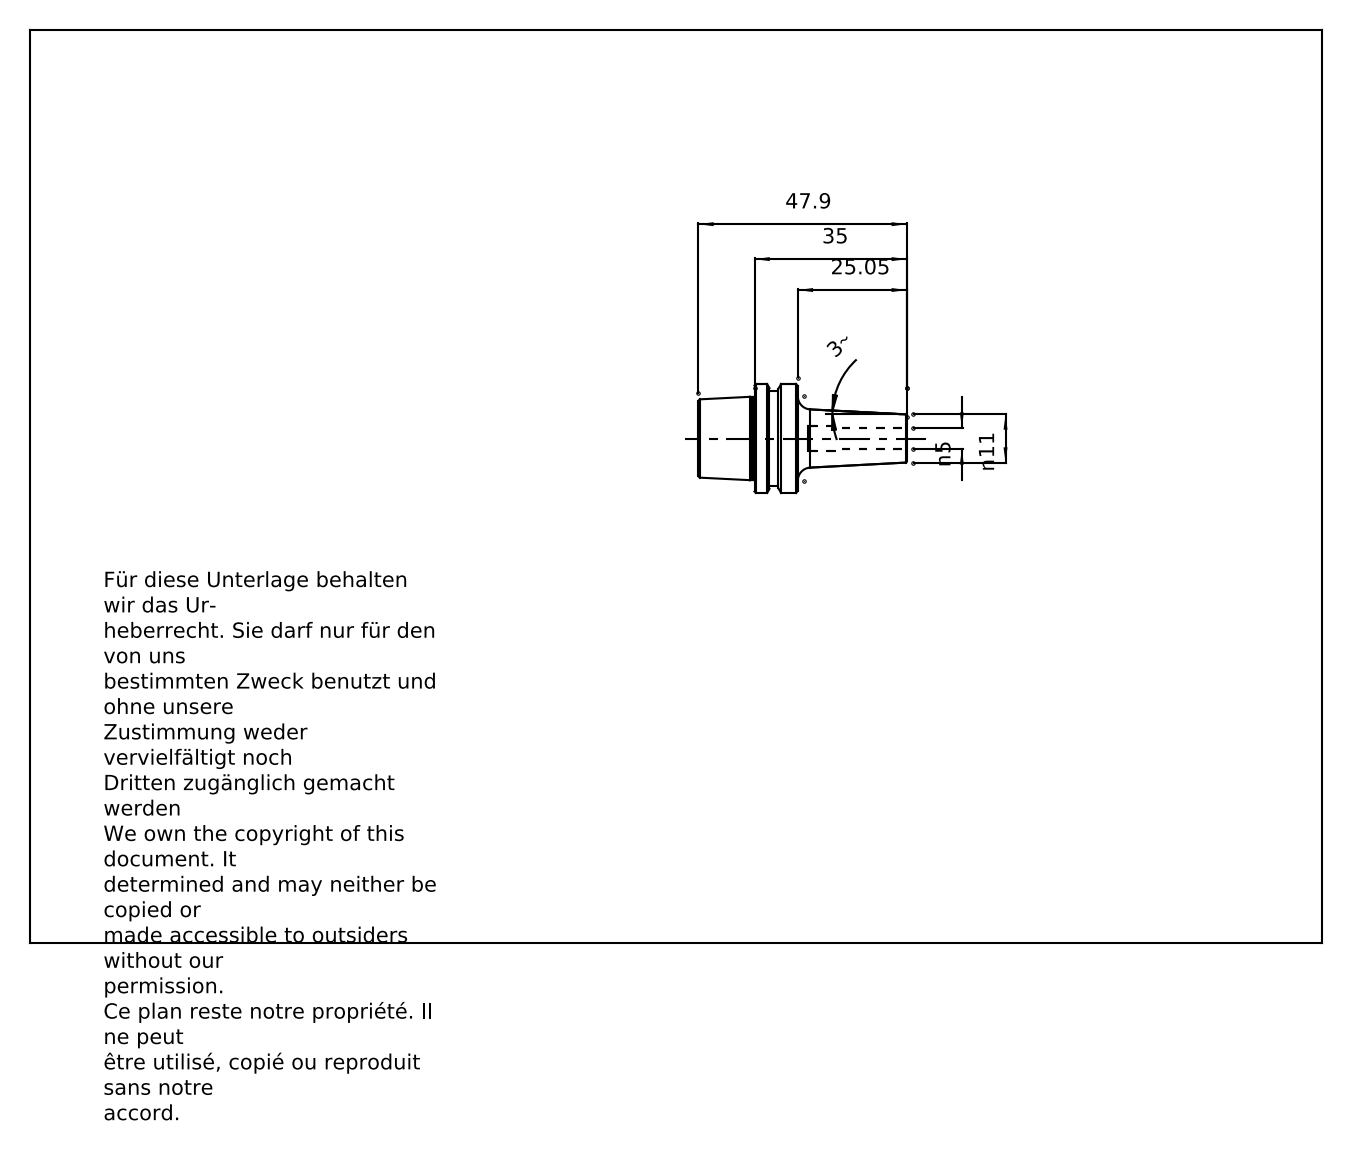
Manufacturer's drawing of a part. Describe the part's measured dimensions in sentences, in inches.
The part is named "E25-185-05". Its 3-D file was written by "PRO/ENGINEER BY PARAMETRIC TECHNOLOGY CORPORATION, 2010430 (CONFIG_CONTROL_DESIGN)". It is 1 solid with 60 faces: 8 planar, 16 cylindrical and 36 other. Overall it measures 1.886 by 0.984 by 0.984 inches. Its volume is 0.453 cubic inches and its surface area 7.378 square inches. Round holes: 1 of diameter 0.197, 1 of diameter 0.553, 1 of diameter 0.648. Round bosses or shafts: 1 of diameter 0.984, 1 of diameter 0.864, 1 of diameter 0.746. The main face-to-face distances are 0.157, 0.234, 0.392, 1.378, 1.144, 0.986, 0.508, 0.742, 0.9, 1.886.
